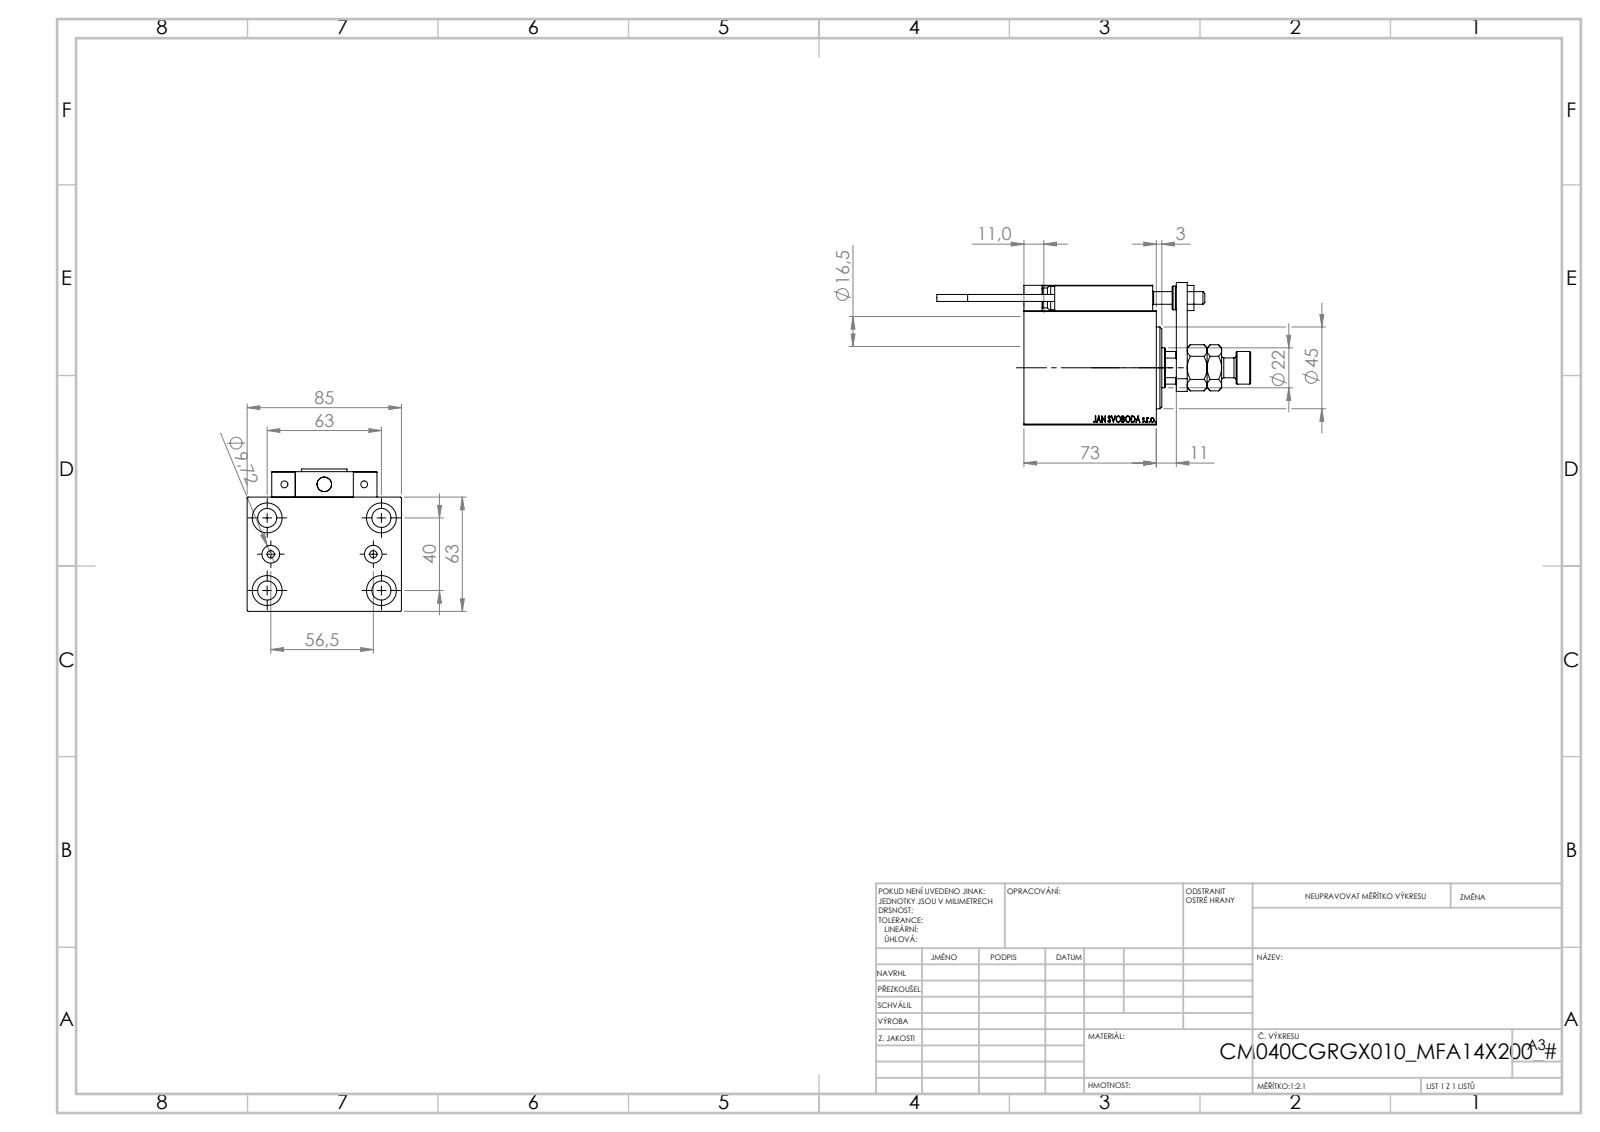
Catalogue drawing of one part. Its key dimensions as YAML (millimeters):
part_name: "SWITCH DIM B,W; V450CM_C_Body; SWITCH_X_FRONT_BACK; X_Y_MFA (+7 more)"
step_written_by: "SolidWorks 2019 (CONFIG_CONTROL_DESIGN)"
units: millimeters
bodies: {solids: 24, faces: 1330, planar: 576, cylindrical: 188, other: 566}
overall_size: [173, 85, 78.5]
volume: 405822
surface_area: 95044
round_holes:
  - {diameter: 4, count: 6}
  - {diameter: 8, count: 5}
  - {diameter: 16.5, count: 5}
  - {diameter: 3.2, count: 4}
  - {diameter: 10.5, count: 4}
  - {diameter: 5, count: 2}
  - {diameter: 9.72, count: 2}
  - {diameter: 7, count: 1}
  - {diameter: 12.5, count: 1}
  - {diameter: 22, count: 1}
  - {diameter: 25.5, count: 1}
  - {diameter: 40, count: 1}
round_bosses_or_shafts:
  - {diameter: 11, count: 2}
  - {diameter: 5, count: 2}
  - {diameter: 3.8, count: 2}
  - {diameter: 18, count: 1}
  - {diameter: 13, count: 1}
partial_cylinders:
  - {radius: 0.3, count: 30}
  - {radius: 3, count: 2}
  - {radius: 10.5, count: 1}
face_to_face_distances: [63, 85, 22, 14, 51, 73, 11, 62, 10, 77]
hole_center_spacings: [37.31, 64.2, 11.37, 20, 20.1, 20.5, 25.08, 29.59]
